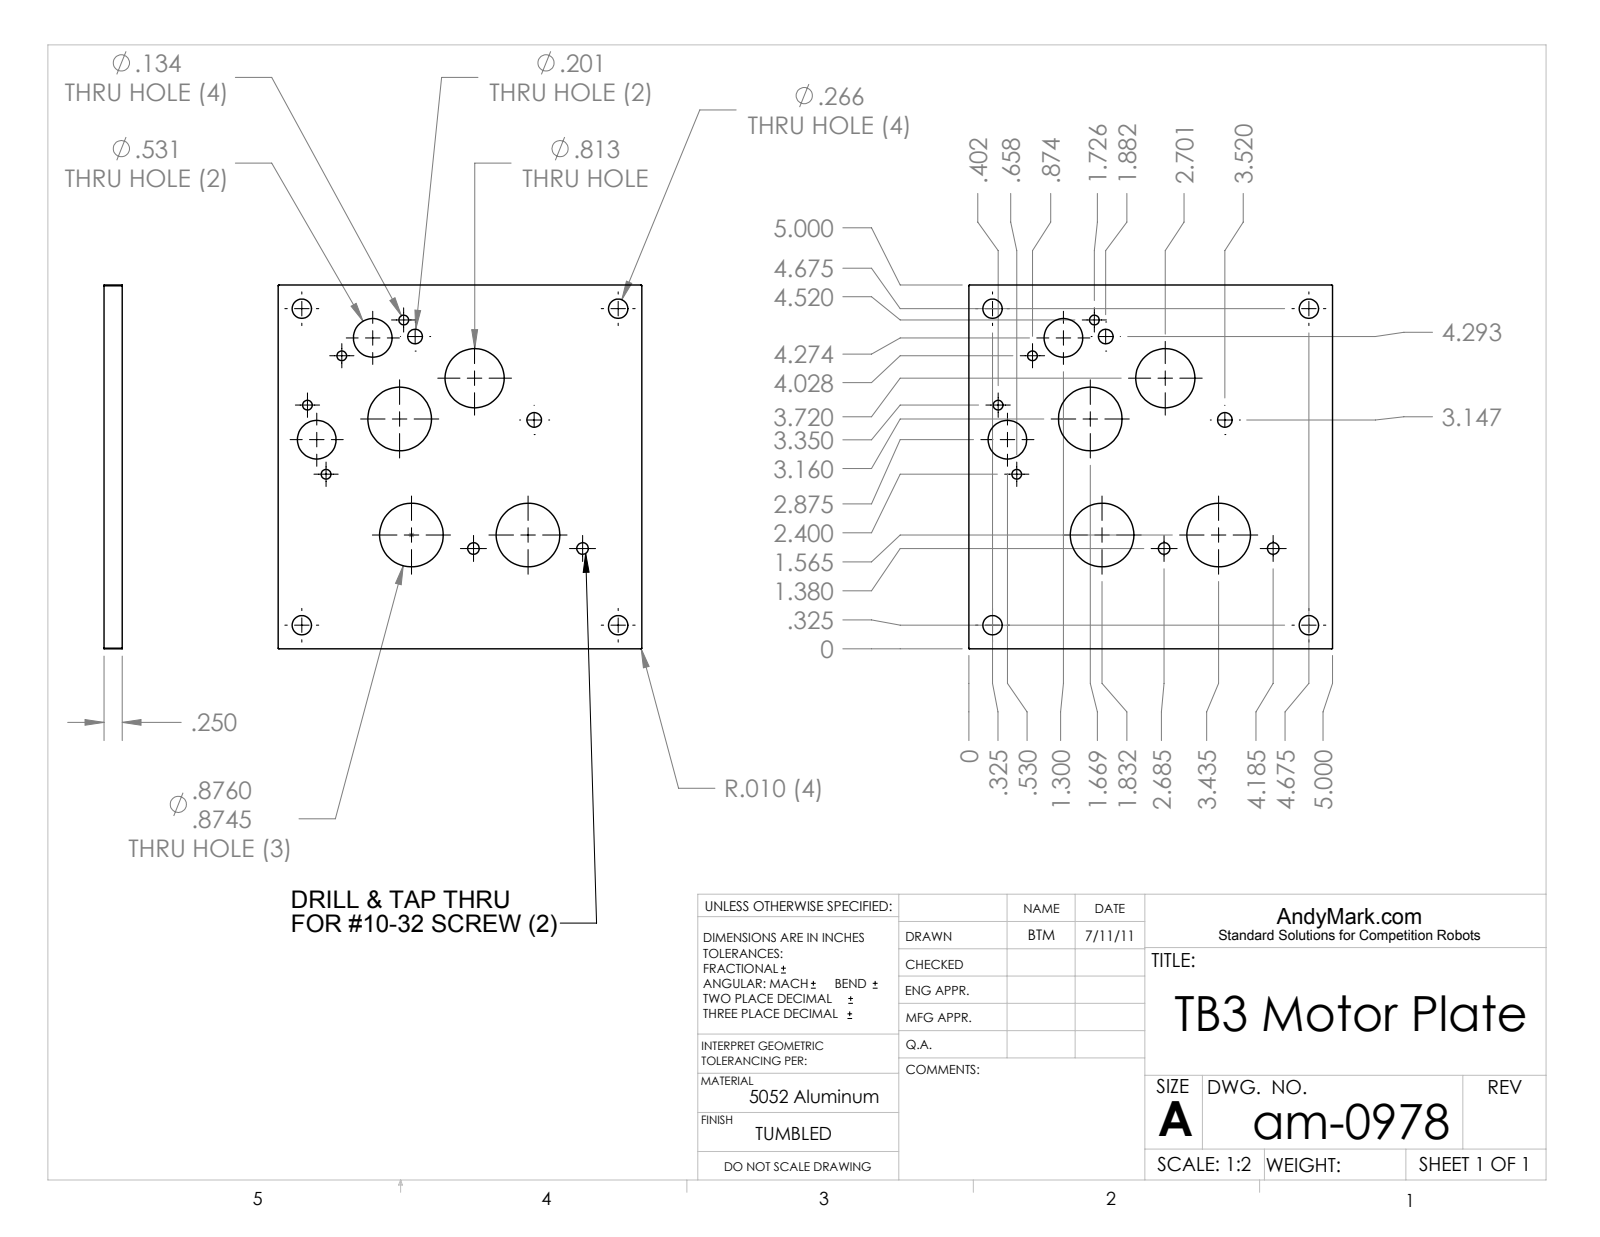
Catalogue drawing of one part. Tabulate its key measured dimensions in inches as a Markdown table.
| quantity | value |
| --- | --- |
| part name | am-0978 TB3 Motor Plate |
| STEP written by | SolidWorks 2010 (AUTOMOTIVE_DESIGN) |
| units | inches |
| bodies | 1 solid, 46 faces (6 planar, 40 cylindrical, 0 other) |
| overall size | 5 × 5 × 0.25 |
| volume | 5.463 in³ |
| surface area | 54.06 in² |
| round holes (diameter × count) | 0.134 × 4, 0.266 × 4, 0.875 × 3, 0.159 × 2, 0.201 × 2, 0.531 × 2, 0.813 × 1 |
| partial cylindrical surfaces (radius × count) | 0.01 × 4 |
| main face-to-face distances | 0.25, 5 |
| hole center spacings | 0.492, 1.603, 0.772, 0.984, 1, 3.208, 4.35, 4.35 |
